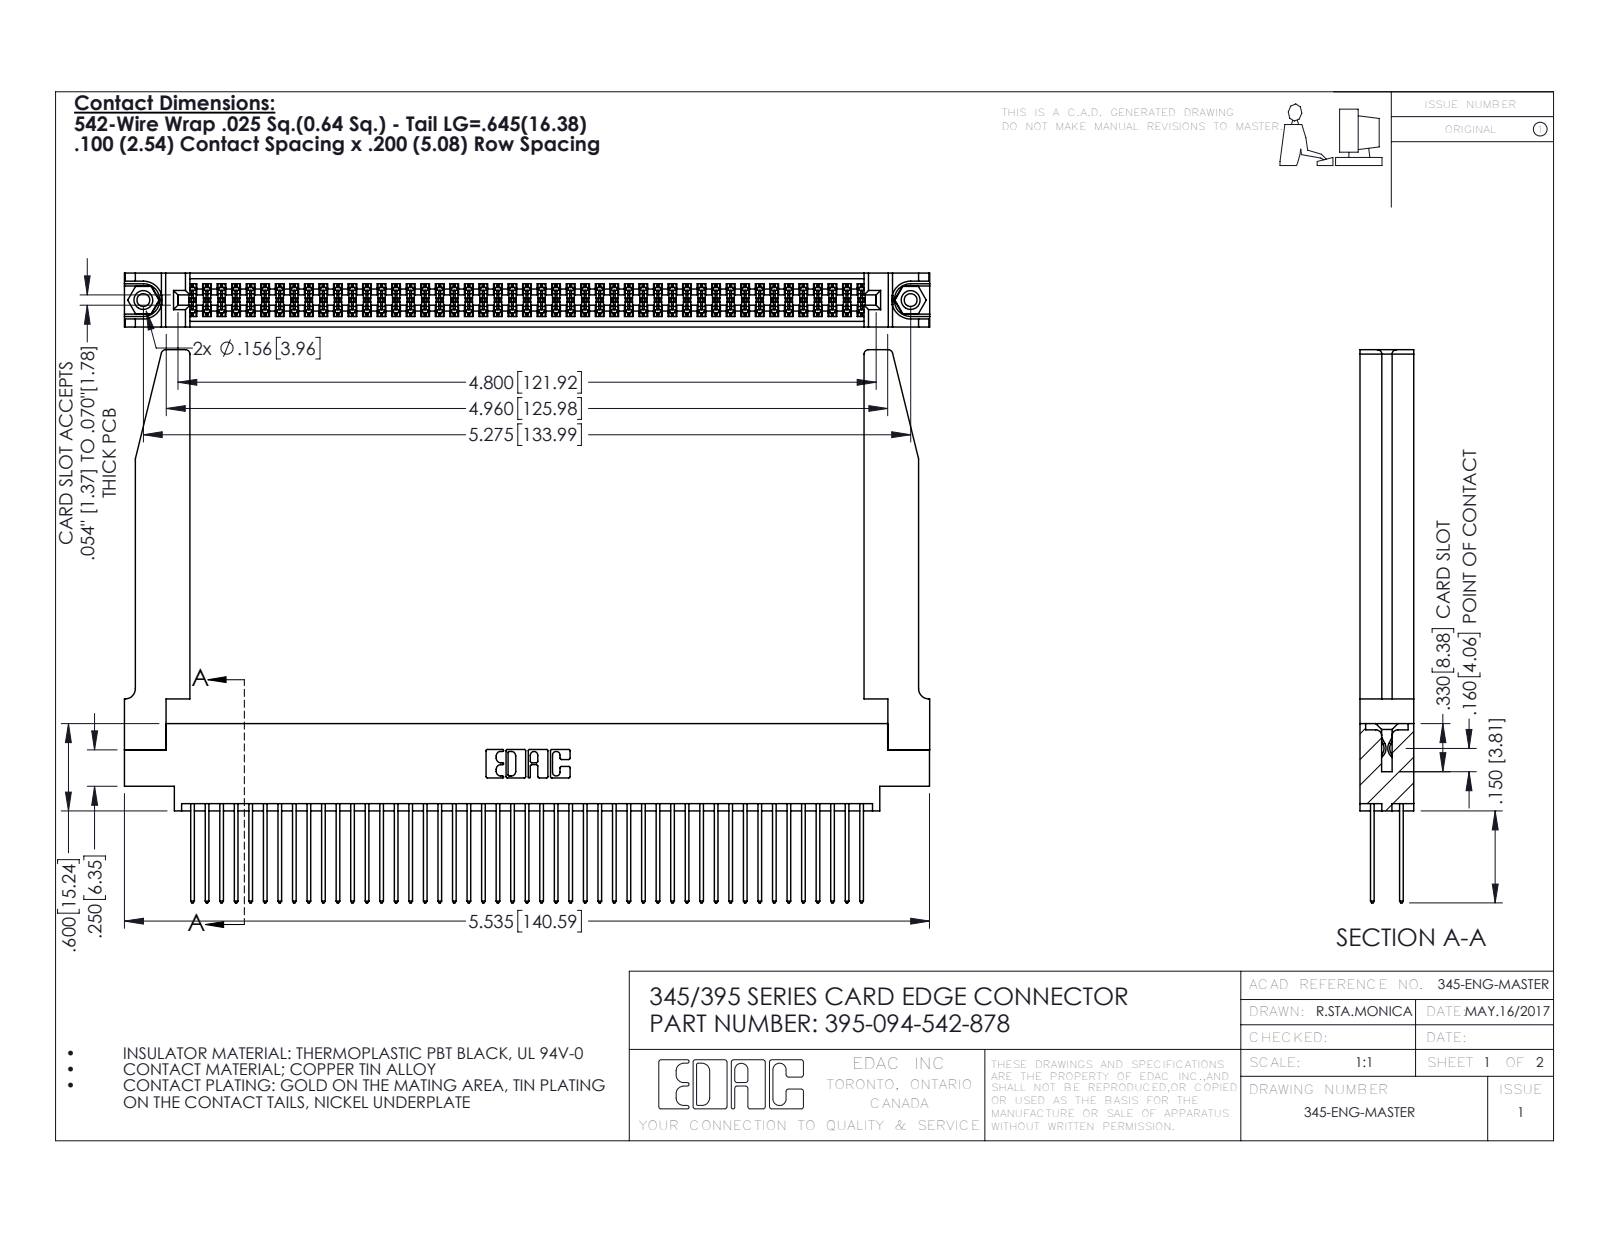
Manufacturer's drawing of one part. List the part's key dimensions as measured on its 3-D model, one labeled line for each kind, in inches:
Part name (STEP PRODUCT): 395-094-542-878; 345-220-078_345-220-078; 345-292-001_345-293-142; 345-250-001_345-250-001-102 (+1 more)
STEP written by: SolidWorks 2016 (CONFIG_CONTROL_DESIGN)
Units: inches
Bodies: 99 solids, 5064 faces (3328 planar, 1684 cylindrical, 52 other)
Overall size (bounding box): 5.536 × 3.802 × 0.37
Volume: 1.33 in³ · Surface area: 46.29 in²
Round holes (diameter × count): ⌀0.089 ×2, ⌀0.125 ×2, ⌀0.156 ×2, ⌀0.064 ×1
Round bosses / shafts (diameter × count): ⌀0.155 ×2
Partial cylindrical surfaces — rounded edges, fillets, slot ends (radius × count): R0.006 ×141, R0.01 ×94, R0.01 ×22, R0.03 ×8, R0.007 ×6, R0.031 ×6, R0.026 ×3, R0.014 ×2
Main face-to-face distances: 0.072, 0.298, 0.37, 0.098, 0.272, 0.025, 0.2, 0.225, 0.175, 0.148
Hole centre spacings: 0.27, 5.039, 5.275
